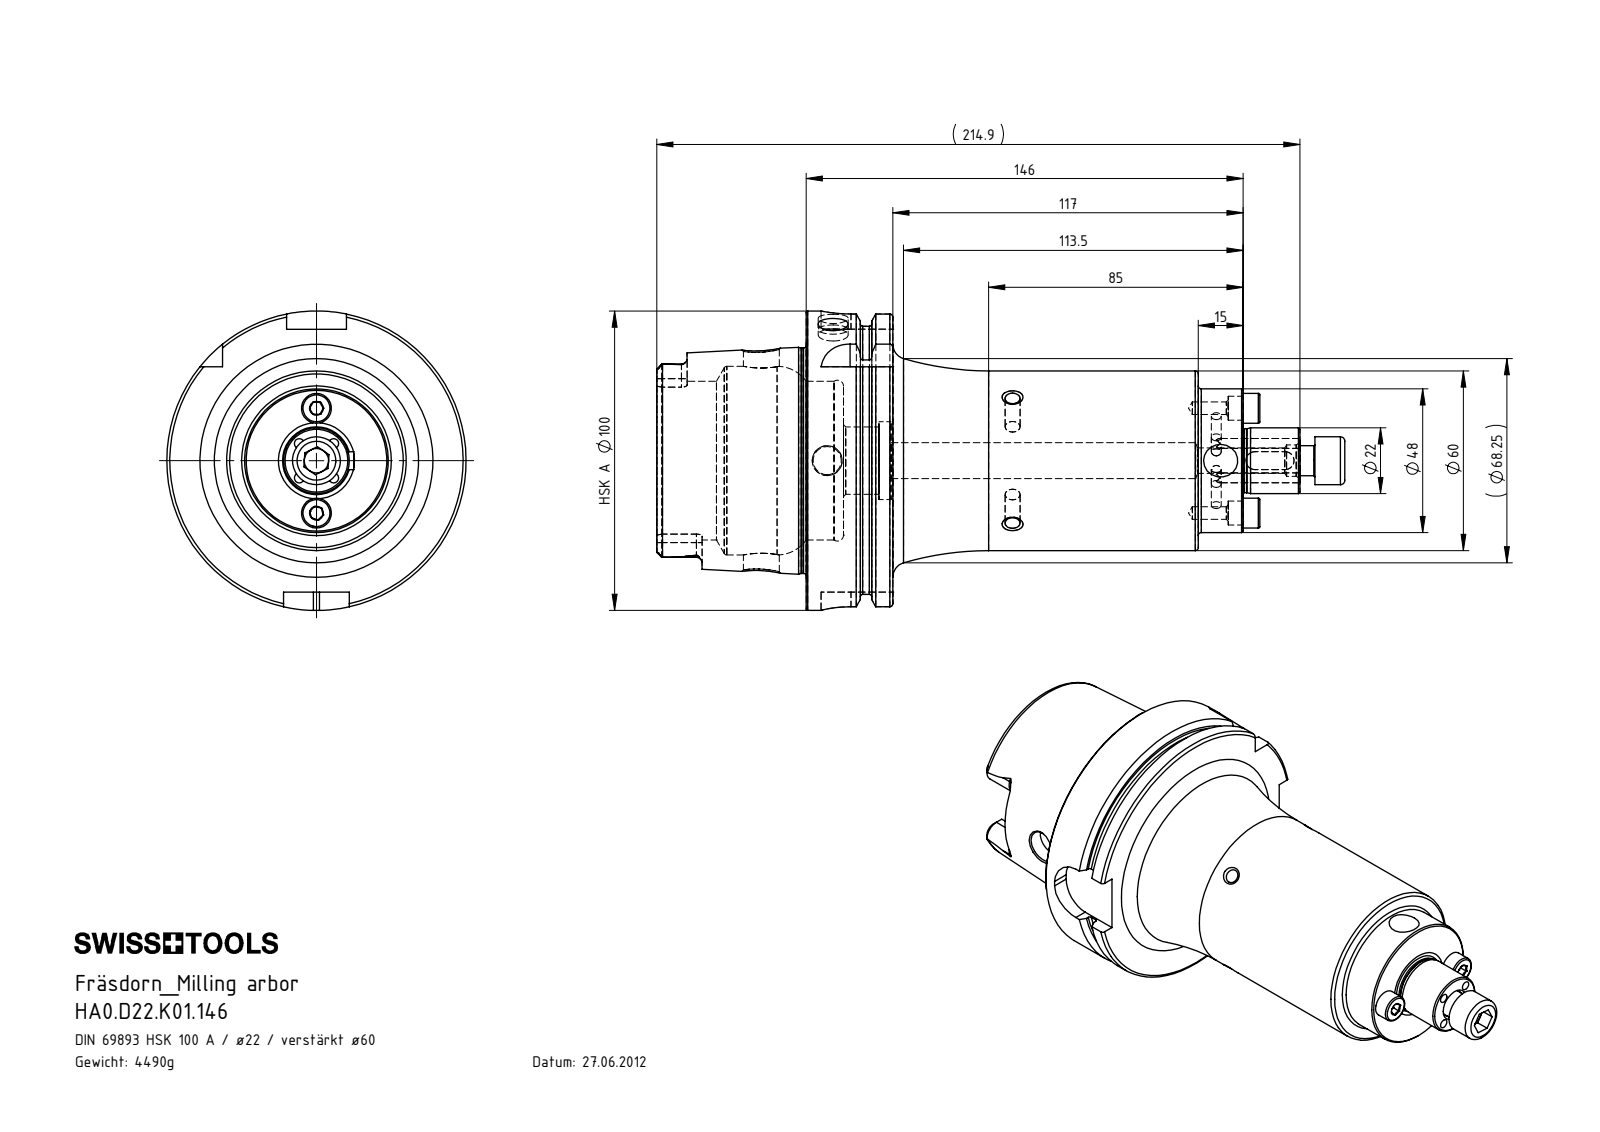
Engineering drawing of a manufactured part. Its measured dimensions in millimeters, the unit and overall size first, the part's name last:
Units: millimetres
Overall size (bounding box): 229.9 × 100 × 100
Round holes (diameter × count): ⌀3.3 ×6, ⌀5 ×4, ⌀10 ×3, ⌀4.2 ×2, ⌀8 ×2, ⌀12 ×2, ⌀8.5 ×1, ⌀10.5 ×1, ⌀22.5 ×1, ⌀26 ×1, ⌀53 ×1, ⌀63 ×1
Round bosses / shafts (diameter × count): ⌀10 ×3, ⌀5 ×2, ⌀3.8 ×2, ⌀100 ×1, ⌀91.95 ×1, ⌀75.26 ×1, ⌀60 ×1, ⌀48 ×1
Partial cylindrical surfaces — rounded edges, fillets, slot ends (radius × count): R1.9 ×6, R3 ×4, R4.88 ×4, R10 ×4
Main face-to-face distances: 28.95, 16.5, 12.45, 146, 133.55, 117.05, 49.9, 62.35, 78.85, 195.9
Hole centre spacings: 8.13, 11.5, 13.08, 23.95, 68.05, 16.26, 17.5, 35
Volume: 575 168 mm³ · Surface area: 82 795 mm²
Bodies: 5 solids, 390 faces (90 planar, 121 cylindrical, 179 other)
Part name (STEP PRODUCT): HA0.D22.K01.146; D22-ER2.001.017_B; DIN 6885 - 6x6x14; ISO 4762 - M10 x 25 (+1 more)
STEP written by: SolidWorks 2017 (AUTOMOTIVE_DESIGN)
